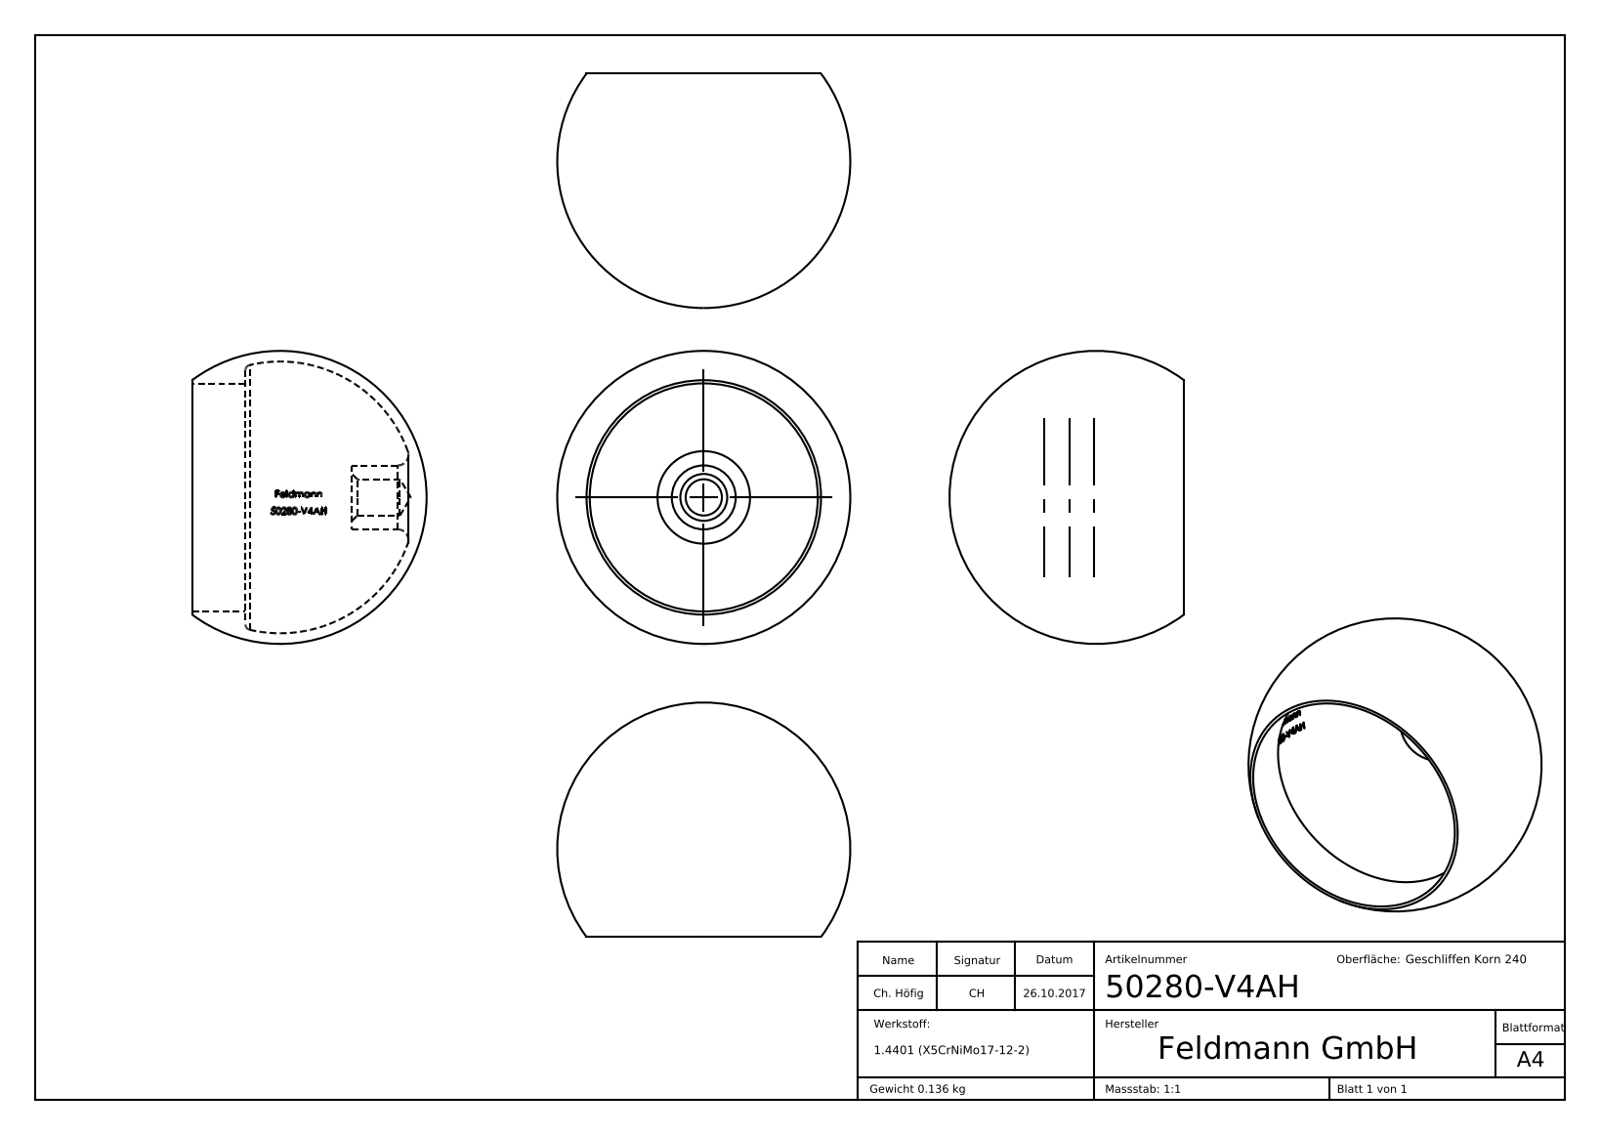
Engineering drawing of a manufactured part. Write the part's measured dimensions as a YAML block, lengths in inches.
part_name: "50280-V4AH"
step_written_by: "SolidWorks 2015 (CONFIG_CONTROL_DESIGN)"
units: inches
bodies: {solids: 1, faces: 258, planar: 116, cylindrical: 6, other: 136}
overall_size: [2.165, 2.165, 1.732]
volume: 1.037
surface_area: 23.48
round_holes:
  - {diameter: 0.268, count: 1}
  - {diameter: 1.685, count: 1}
round_bosses_or_shafts:
  - {diameter: 0.472, count: 1}
face_to_face_distances: [0.394, 0.787, 1.181, 0.131, 0.075, 0.26, 0.106, 0.121, 0.126, 0.191]
